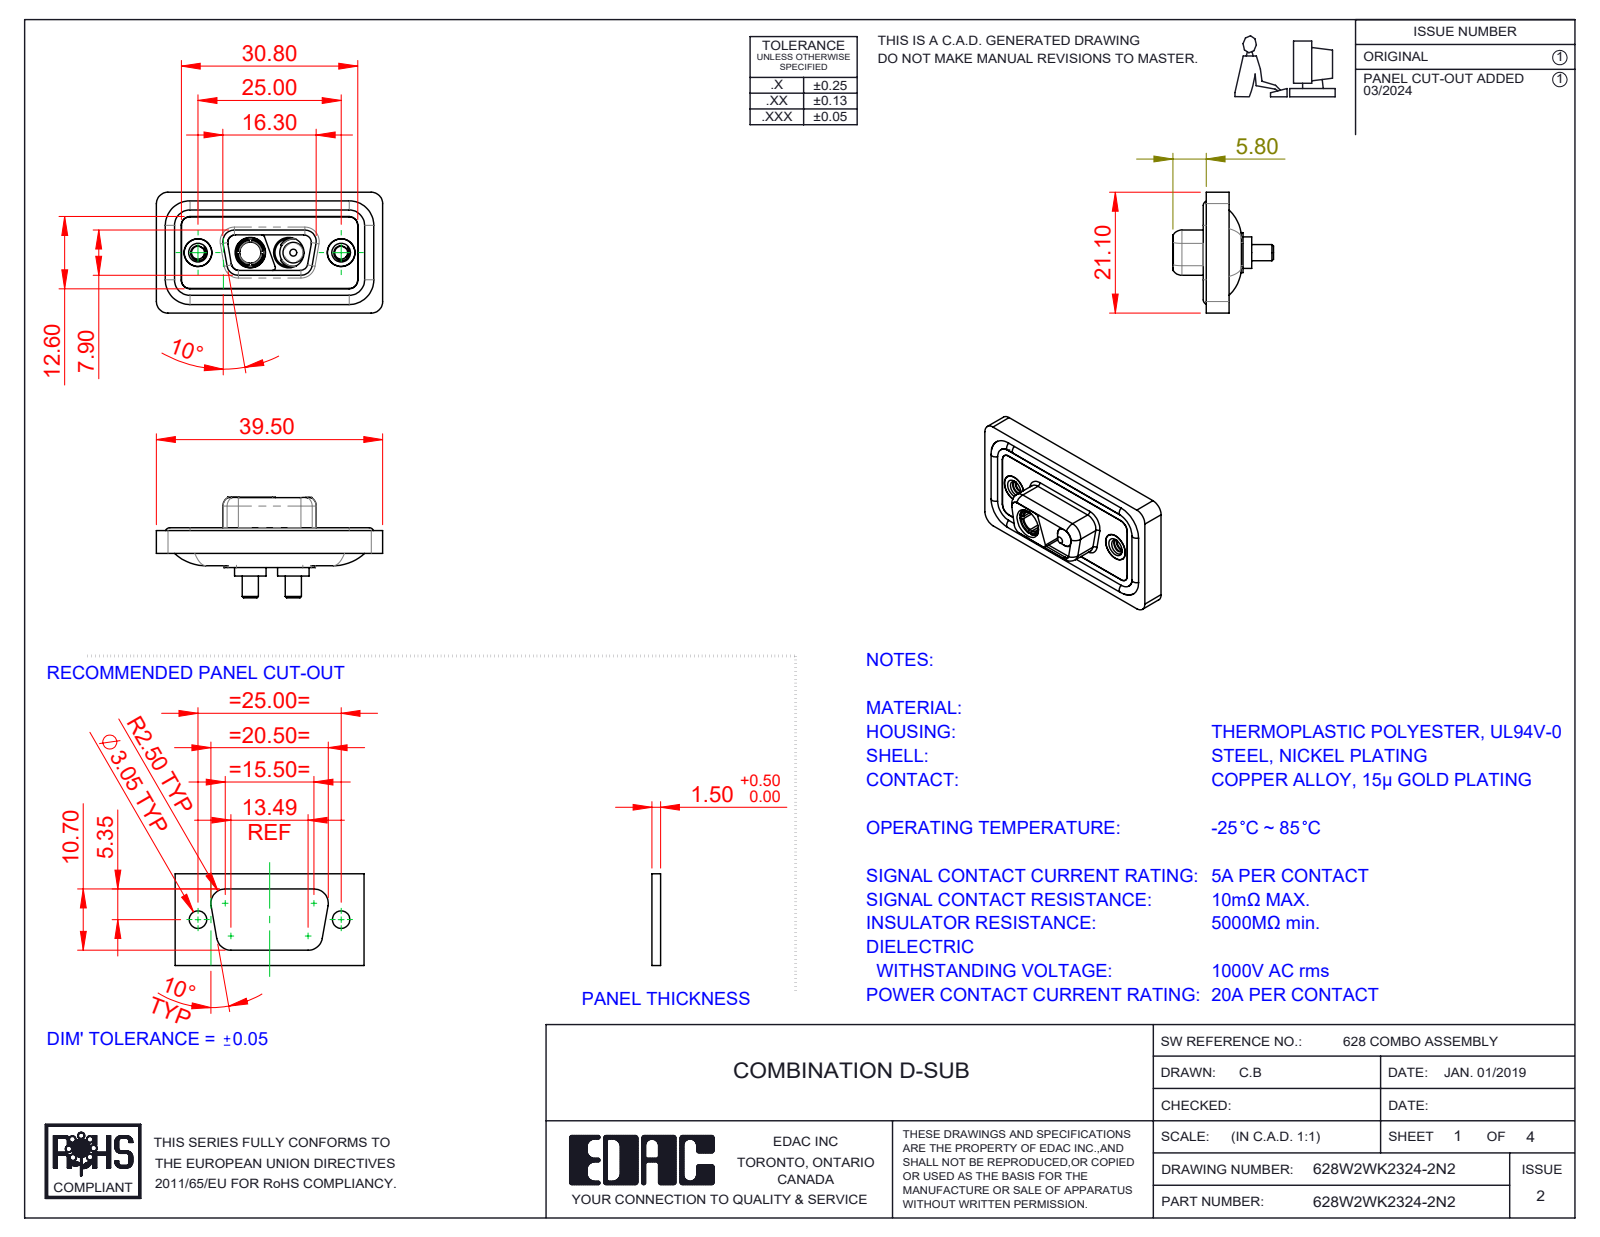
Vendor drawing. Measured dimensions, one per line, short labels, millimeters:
name: 628Combo Shell Rear_09 Contacts; Power Pin_20A S; 628W2WK2324-2N2; 628Combo Housing_2WK2 (+4 more)
written by: SolidWorks 2023 (CONFIG_CONTROL_DESIGN)
unit: mm
bodies: 11 solids, 500 faces (144 planar, 231 cylindrical, 125 other)
size: 39.5 × 21.1 × 17.55
volume: 4 603 mm³; area: 7 344 mm²
holes: 4× ⌀4.85, 2× ⌀2.26, 2× ⌀4, 2× ⌀4.05, 2× ⌀5, 2× ⌀5.3, 1× ⌀3.7
bosses: 4× ⌀1.6, 2× ⌀5.5, 2× ⌀5.2, 2× ⌀4.95, 2× ⌀4.8, 2× ⌀4.75, 2× ⌀3.75, 2× ⌀2.8
rounds: 22× R1.5, 18× R2, 8× R1.35, 8× R1.6, 6× R0.5, 4× R0.25, 4× R0.6, 4× R0.65
face distances: 0.4, 1.1, 2.9, 1.6, 0.5, 1.8, 5.65, 1.5, 5.35, 3.1
hole spacings: 9.14, 15.86, 6.72, 25
